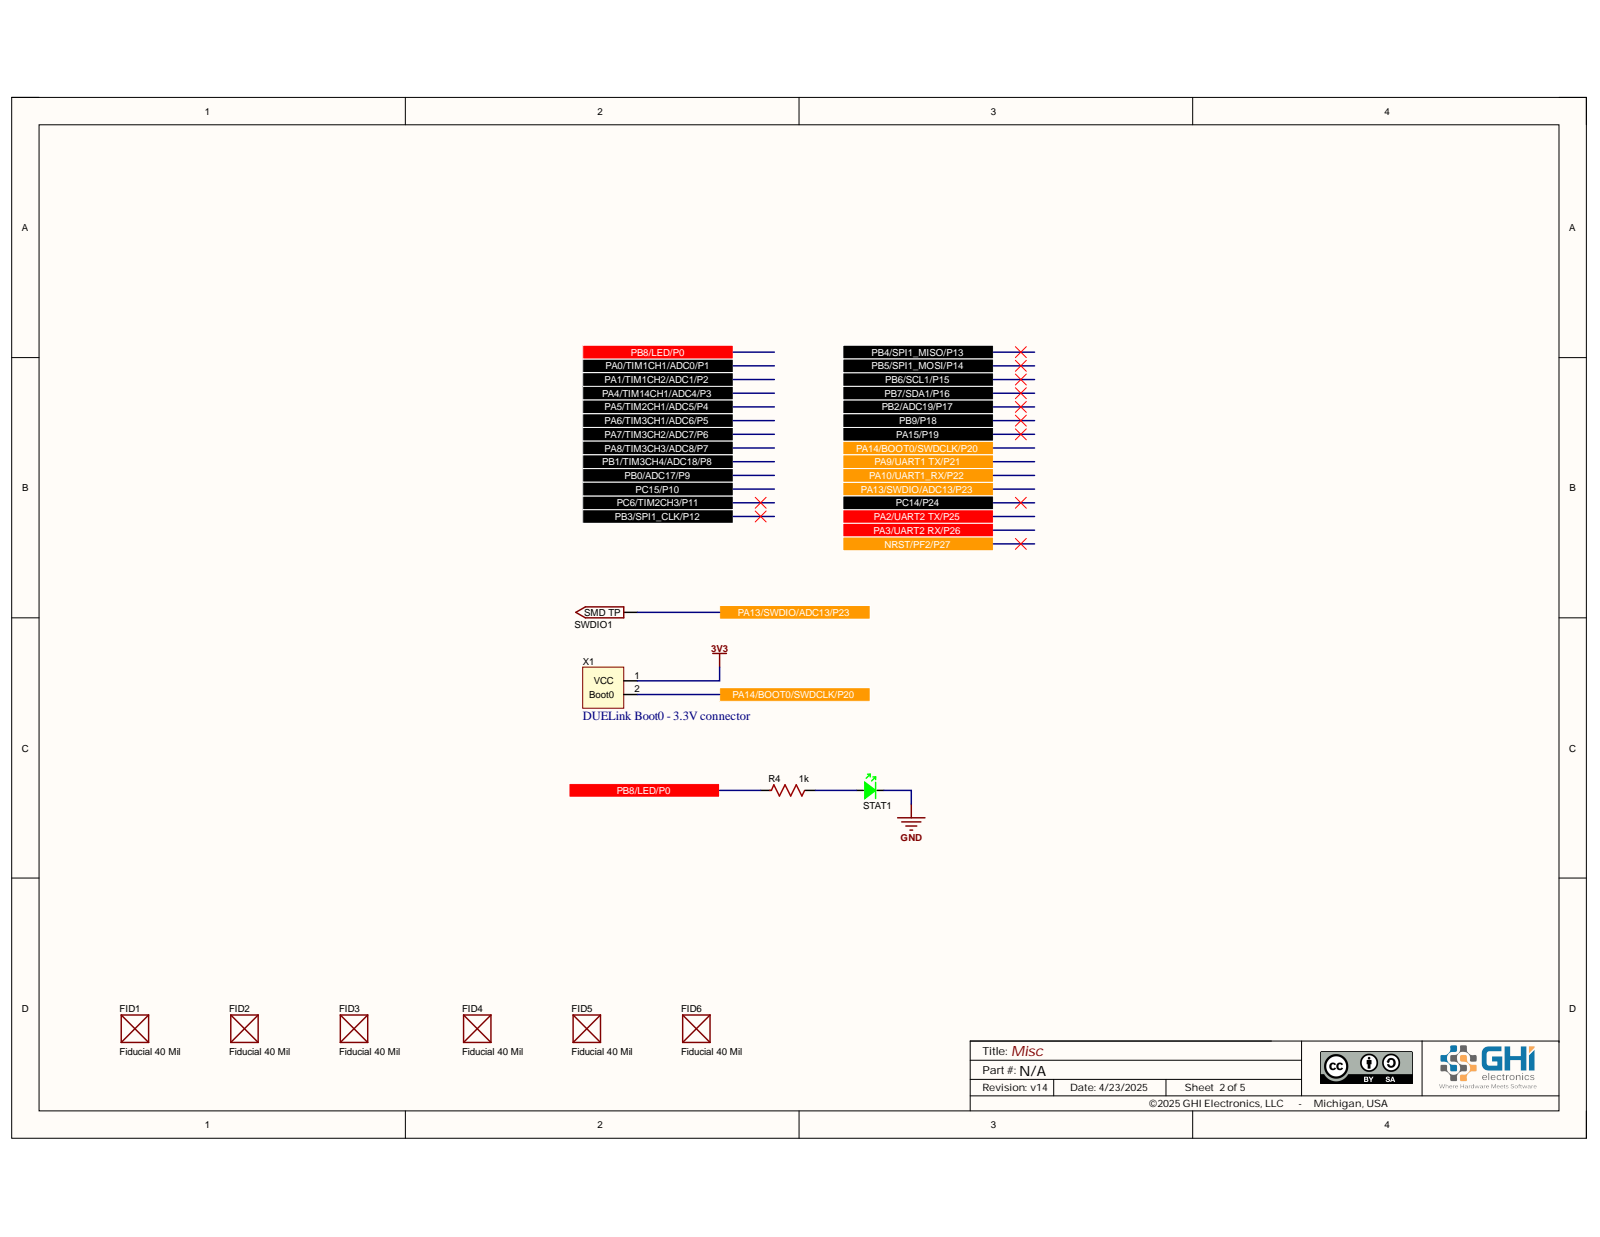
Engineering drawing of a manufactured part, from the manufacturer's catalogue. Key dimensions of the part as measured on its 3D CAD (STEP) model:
Part name (STEP PRODUCT): PCB; Board; STAT1; 0603 LED Green (+5 more)
STEP written by: Open CASCADE 7.5 (AUTOMOTIVE_DESIGN)
Units: millimetres
Bodies: 93 solids, 6090 faces (4987 planar, 703 cylindrical, 400 other)
Overall size (bounding box): 87 × 65 × 22.48
Volume: 87 178 mm³ · Surface area: 42 620 mm²
Round holes (diameter × count): ⌀1.1 ×10, ⌀1 ×8, ⌀2.3 ×4, ⌀3 ×4, ⌀1.02 ×2
Partial cylindrical surfaces — rounded edges, fillets, slot ends (radius × count): R0.5 ×64, R0.12 ×35, R0.15 ×14, R0.2 ×8, R23.96 ×8, R0.1 ×4, R2.5 ×4, R3.5 ×4
Main face-to-face distances: 7.2, 16.4, 9.2, 9, 16.2, 12.7, 12.5, 3.5, 3.7, 2.55
Hole centre spacings: 2.54, 5.08, 7.62, 10.16, 12.7, 15.24, 17.78, 10.44
